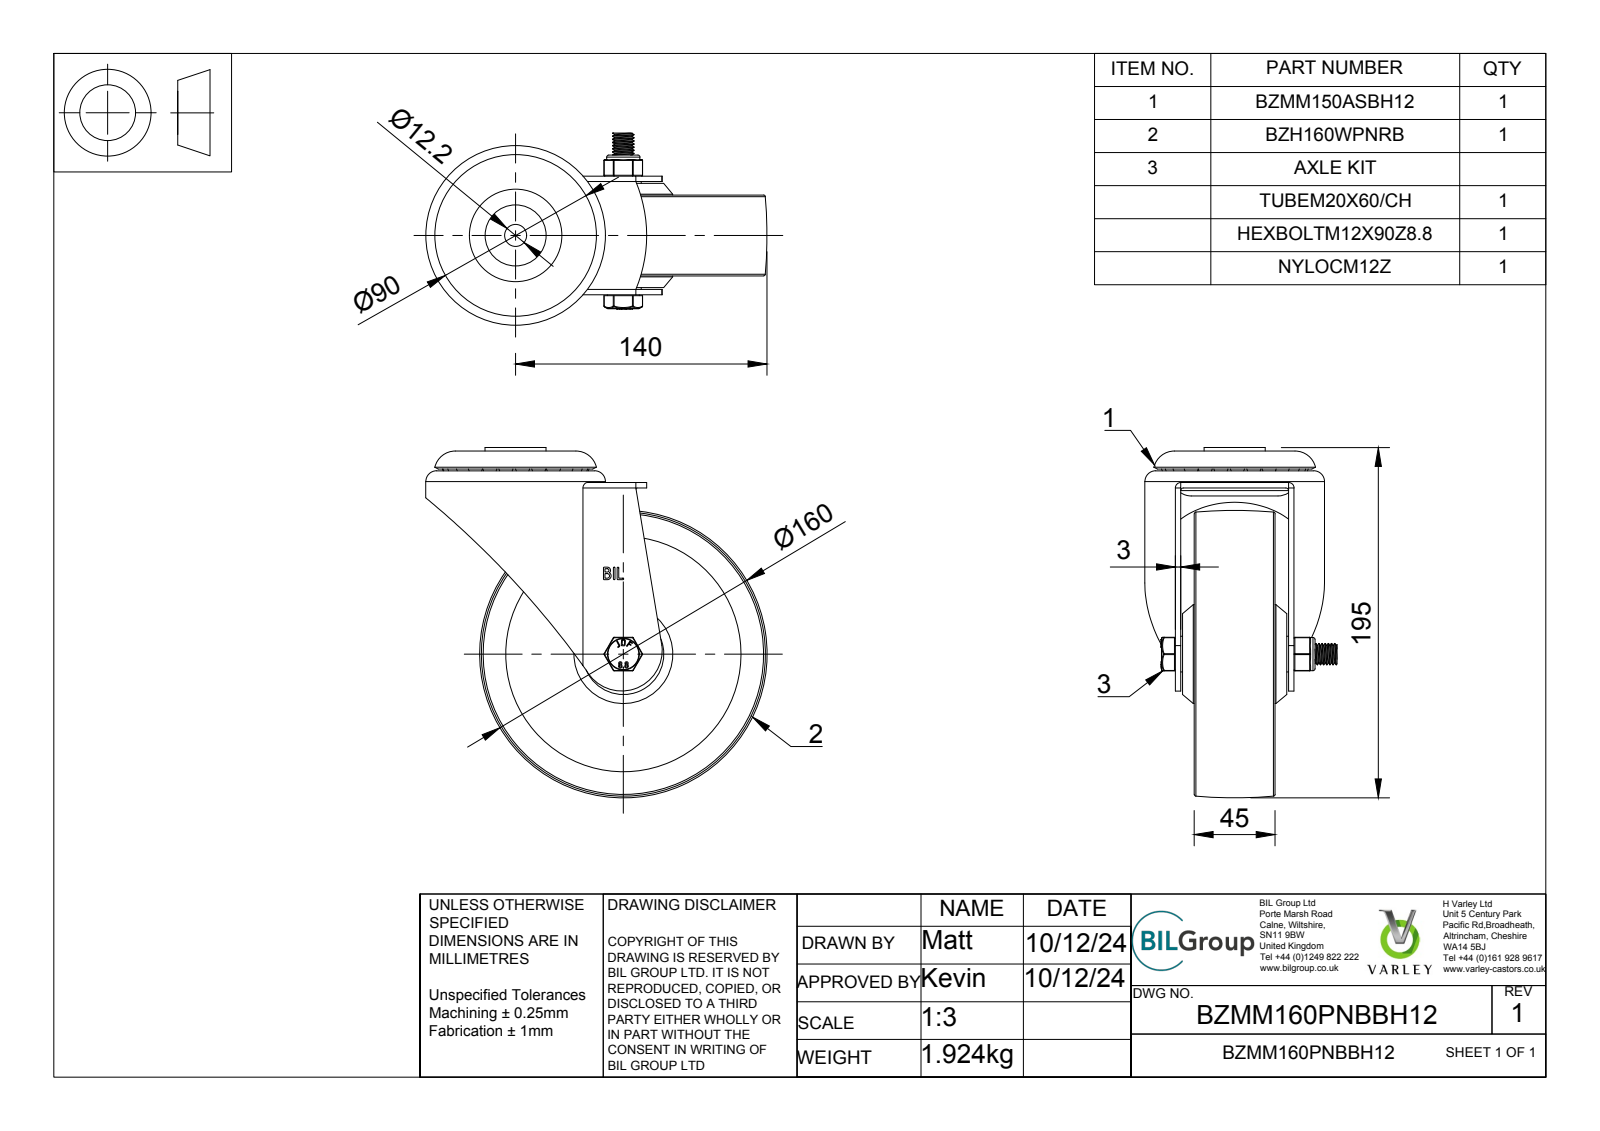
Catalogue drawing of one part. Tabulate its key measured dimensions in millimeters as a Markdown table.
| quantity | value |
| --- | --- |
| part name | BZMM160PNBBH12 v3; BZMM150ASBH12 v1; ZINC PLATED, PRESSED STEEL FORKS; ZINC PLATED, PRESSED STEEL HEAD (+6 more) |
| STEP written by | Autodesk Translation Framework v13.20.0.188 (AP242_MANAGED_MODEL_BASED_3D_ENGINEERING_MIM_LF) |
| units | millimeters |
| bodies | 65 solids, 502 faces (211 planar, 161 cylindrical, 130 other) |
| overall size | 195 × 190 × 107 |
| volume | 703 797 mm³ |
| surface area | 244 139 mm² |
| round holes (diameter × count) | 12 × 1, 12.2 × 1, 12.5 × 1, 14 × 1, 20.5 × 1, 30 × 1, 33 × 1, 39 × 1, 58 × 1, 94 × 1, 131 × 1, 135 × 1 |
| round bosses / shafts (diameter × count) | 5 × 10, 100 × 1, 63 × 1, 55 × 1, 34 × 1, 32.9 × 1, 29.5 × 1, 24 × 1 |
| partial cylindrical surfaces (radius × count) | 0.5 × 20, 0.47 × 4, 0.9 × 4, 1.5 × 4, 0.89 × 2, 0.89 × 2, 3 × 2, 6.78 × 2 |
| main face-to-face distances | 3, 12, 10.5, 52.5, 16.5, 28.5, 39, 7.5, 27, 55.5 |
